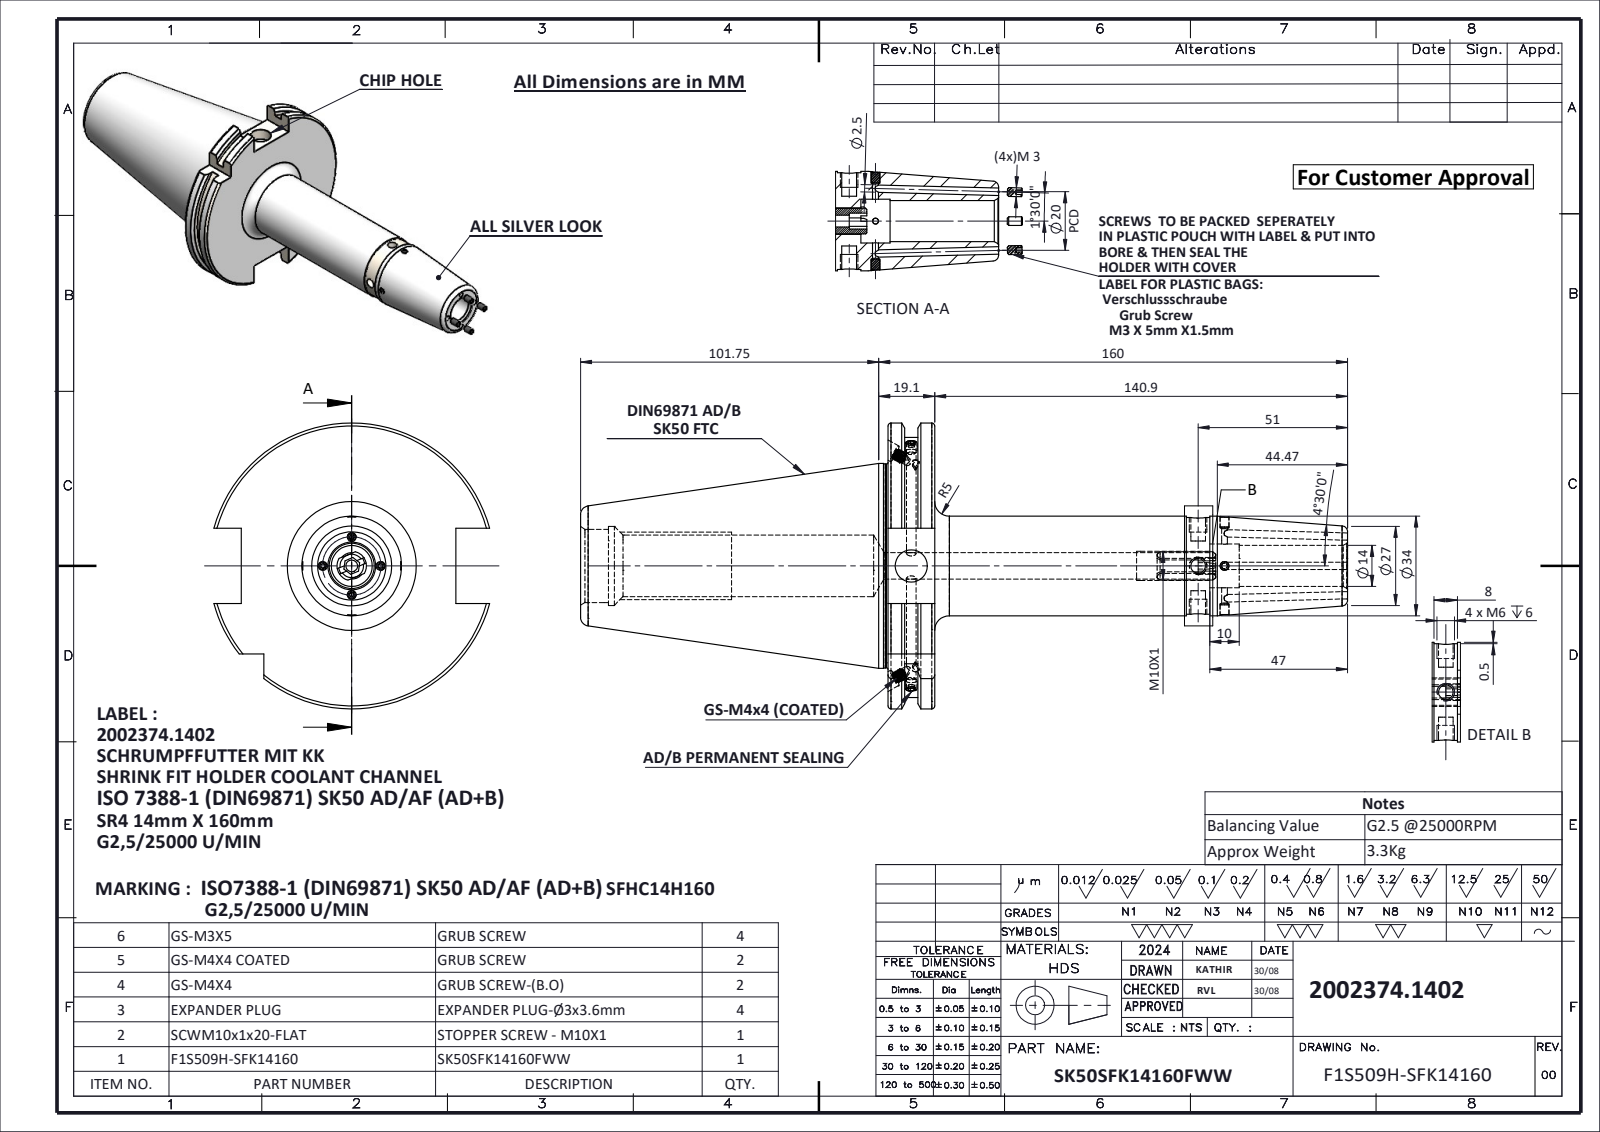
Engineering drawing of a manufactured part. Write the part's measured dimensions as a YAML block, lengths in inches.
part_name: "SK50SFK14160FWW; SCWM10x1x20-FLAT&SLOT_REWORK; GS-M4X4-COATING_DIN 913 - M4 x 4-N; GS-M3X5 (+3 more)"
step_written_by: "SolidWorks 2024 (CONFIG_CONTROL_DESIGN)"
units: inches
bodies: {solids: 14, faces: 452, planar: 151, cylindrical: 131, other: 170}
overall_size: [10.621, 3.839, 3.703]
volume: 26.24
surface_area: 104.2
round_holes:
  - {diameter: 0.098, count: 4}
  - {diameter: 0.079, count: 2}
  - {diameter: 0.118, count: 2}
  - {diameter: 0.126, count: 2}
  - {diameter: 0.197, count: 2}
  - {diameter: 0.236, count: 2}
  - {diameter: 0.13, count: 1}
  - {diameter: 0.157, count: 1}
  - {diameter: 0.354, count: 1}
  - {diameter: 0.433, count: 1}
  - {diameter: 0.55, count: 1}
  - {diameter: 0.59, count: 1}
round_bosses_or_shafts:
  - {diameter: 0.157, count: 4}
  - {diameter: 0.118, count: 4}
  - {diameter: 0.114, count: 2}
  - {diameter: 2.75, count: 1}
  - {diameter: 2.734, count: 1}
  - {diameter: 1.339, count: 1}
  - {diameter: 1.299, count: 1}
partial_cylinders:
  - {radius: 0.197, count: 1}
  - {radius: 1.768, count: 1}
  - {radius: 1.919, count: 1}
face_to_face_distances: [0.626, 0.223, 0.403, 0.399, 0.176, 0.227, 4.132, 4.355, 4.531, 4.758]
hole_center_spacings: [0.354, 3.854, 4.209]
